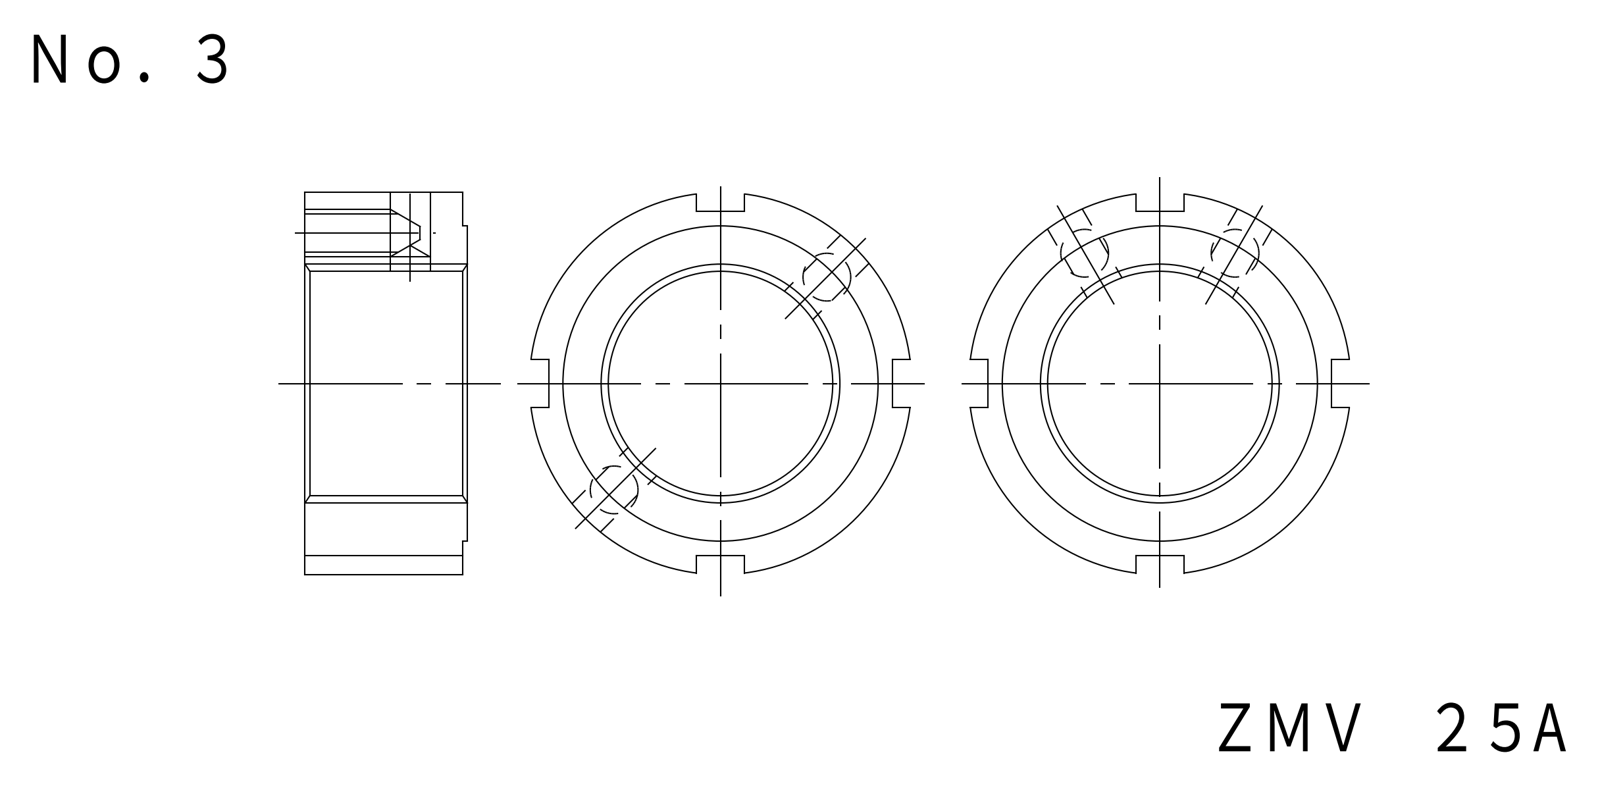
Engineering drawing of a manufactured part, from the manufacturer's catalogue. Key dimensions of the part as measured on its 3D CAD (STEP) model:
Part name (STEP PRODUCT): FKD ZMV25A
STEP written by: Autodesk Inventor LT (CONFIG_CONTROL_DESIGN)
Units: millimetres
Bodies: 1 solid, 25 faces (15 planar, 10 cylindrical, 0 other)
Overall size (bounding box): 39.69 × 39.69 × 17
Volume: 11 719 mm³ · Surface area: 5 489 mm²
Round holes (diameter × count): ⌀4.13 ×2, ⌀4.2 ×2, ⌀25 ×1
Round bosses / shafts (diameter × count): ⌀40 ×1, ⌀33 ×1
Main face-to-face distances: 17, 0.5, 16.5, 15.5, 20.5, 36, 5
Hole centre spacings: 15.75, 31.51
